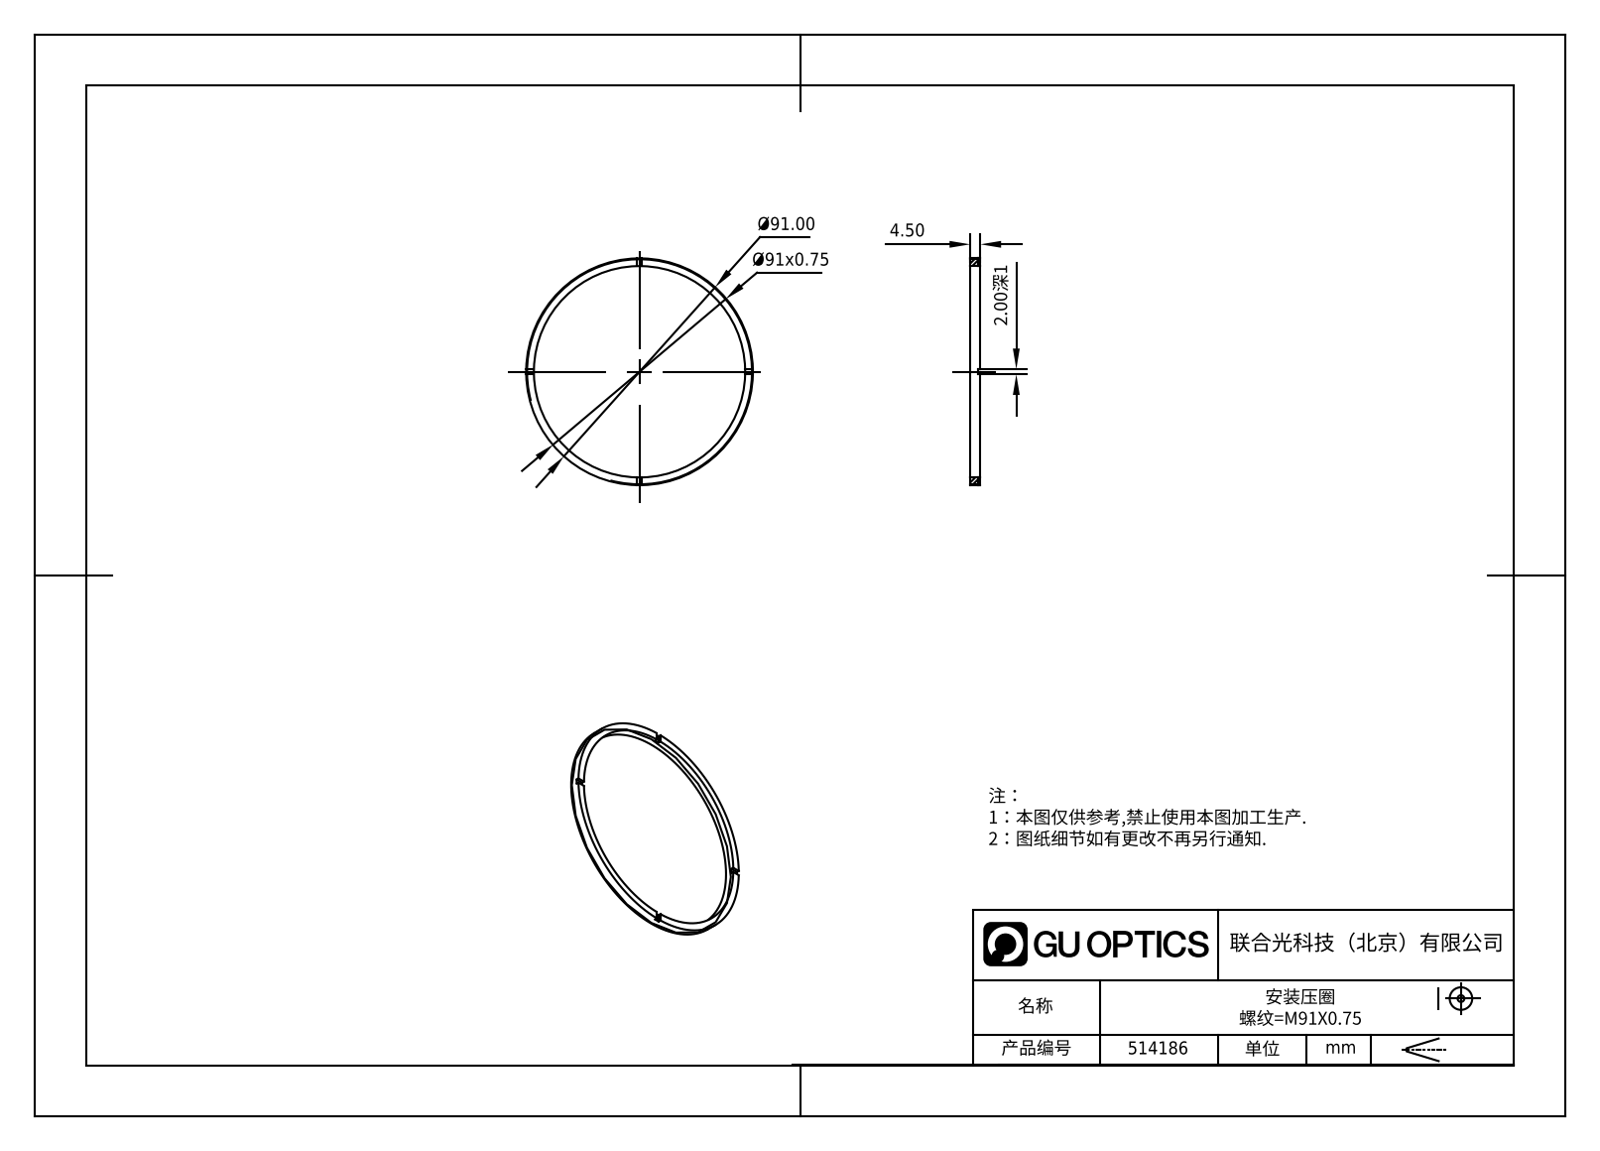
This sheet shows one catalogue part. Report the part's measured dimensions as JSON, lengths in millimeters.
{"part_name": "514186", "step_written_by": "SolidWorks 2020 (CONFIG_CONTROL_DESIGN)", "units": "millimeters", "bodies": {"solids": 1, "faces": 21, "planar": 17, "cylindrical": 4, "other": 0}, "overall_size": [91, 91, 4.5], "volume_mm3": 4302, "surface_area_mm2": 4410, "round_holes": [[84, 1]], "round_bosses_or_shafts": [[91, 1]], "face_to_face_distances": [4.5, 3.5, 1, 2]}
